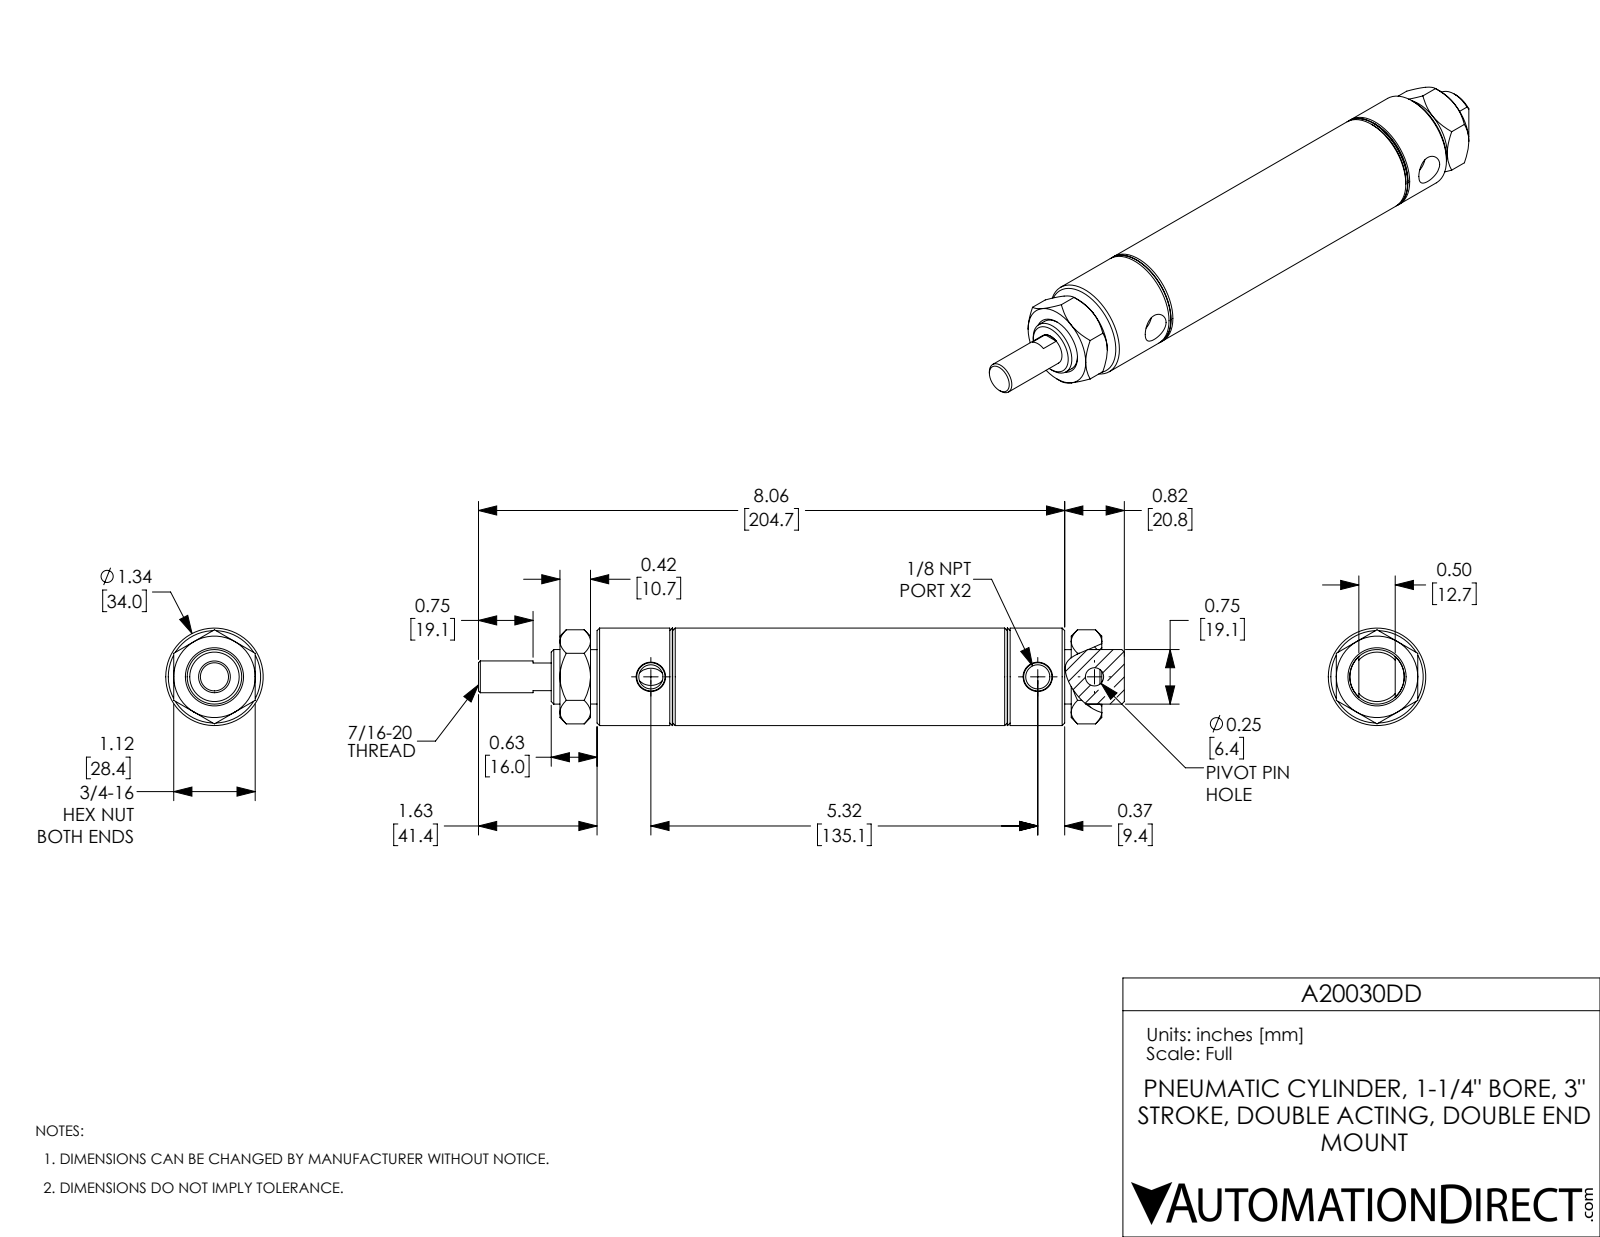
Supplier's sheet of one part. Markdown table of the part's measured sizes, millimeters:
| quantity | value |
| --- | --- |
| part name | A20030DD_Mounting Nut_D-3556; A20030DD-Rod; A20030DD-MainBody; A20030DD |
| STEP written by | SolidWorks 2017 (AUTOMOTIVE_DESIGN) |
| units | millimeters |
| bodies | 4 solids, 138 faces (44 planar, 36 cylindrical, 58 other) |
| overall size | 225.6 × 34 × 34 |
| volume | 113 700 mm³ |
| surface area | 47 660 mm² |
| round holes (diameter × count) | 8.4 × 2, 6.4 × 1, 11.1 × 1, 19.1 × 1, 31.8 × 1 |
| round bosses / shafts (diameter × count) | 34 × 1, 19 × 1 |
| main face-to-face distances | 37.2, 126.1, 12.7, 28.4, 88.9, 76.2, 7.9, 10.7, 178.6, 49.9 |
| hole center spacings | 19.8, 135.1, 154.9 |
